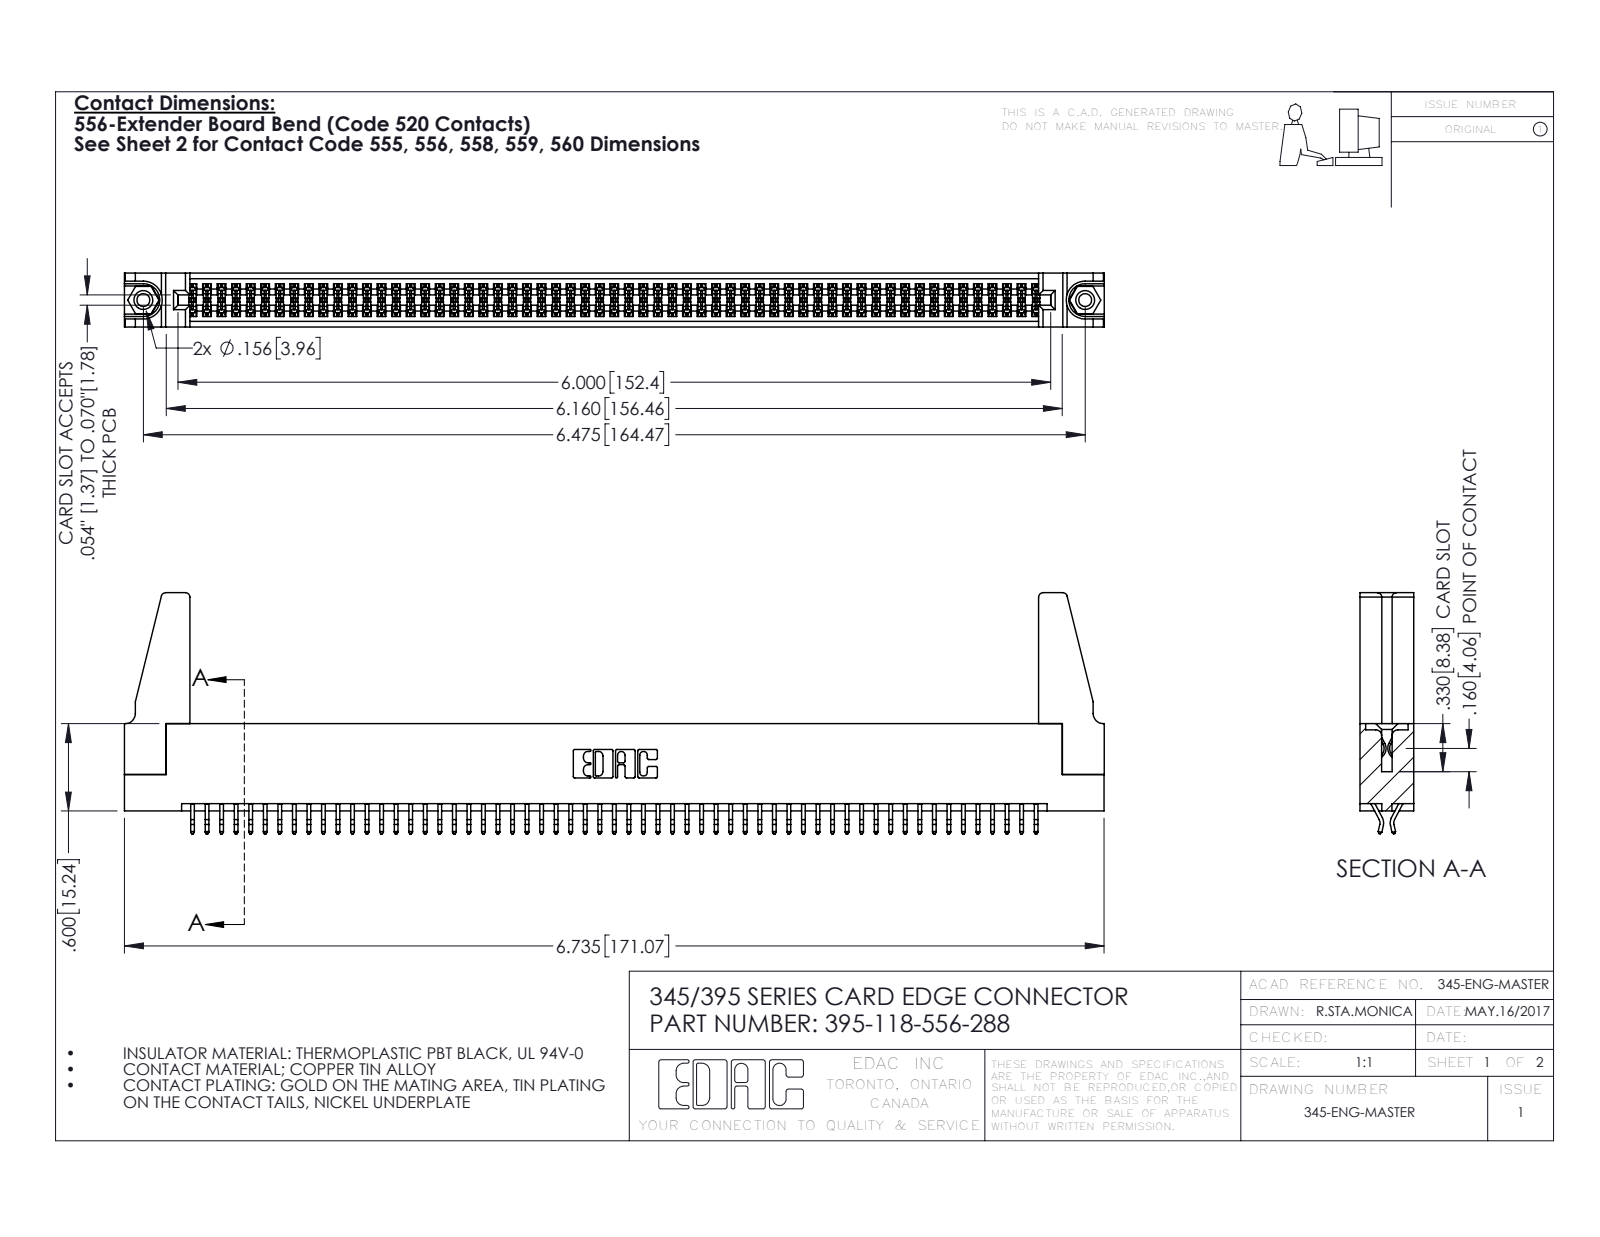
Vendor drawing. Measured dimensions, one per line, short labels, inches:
name: 345 Part_Flush Mounting Lugs - 0.156 Dia-TH; 345-250-001_345-250-001-102; 345-292-001_556 Tail; 345-220-078_345-220-088 (+1 more)
written by: SolidWorks 2016 (CONFIG_CONTROL_DESIGN)
unit: in
bodies: 122 solids, 6855 faces (4515 planar, 2324 cylindrical, 16 other)
size: 6.736 × 1.657 × 0.37
volume: 0.269 in³; area: 43.59 in²
holes: 2× ⌀0.089, 2× ⌀0.125, 2× ⌀0.156, 1× ⌀0.064
bosses: 2× ⌀0.155
rounds: 177× R0.006, 22× R0.01, 8× R0.03, 6× R0.007, 6× R0.031, 3× R0.026, 2× R0.01, 2× R0.014
face distances: 0.072, 0.298, 0.37, 0.2, 0.025, 0.098, 0.272, 0.225, 0.175, 0.149
hole spacings: 0.27, 6.239, 6.475
